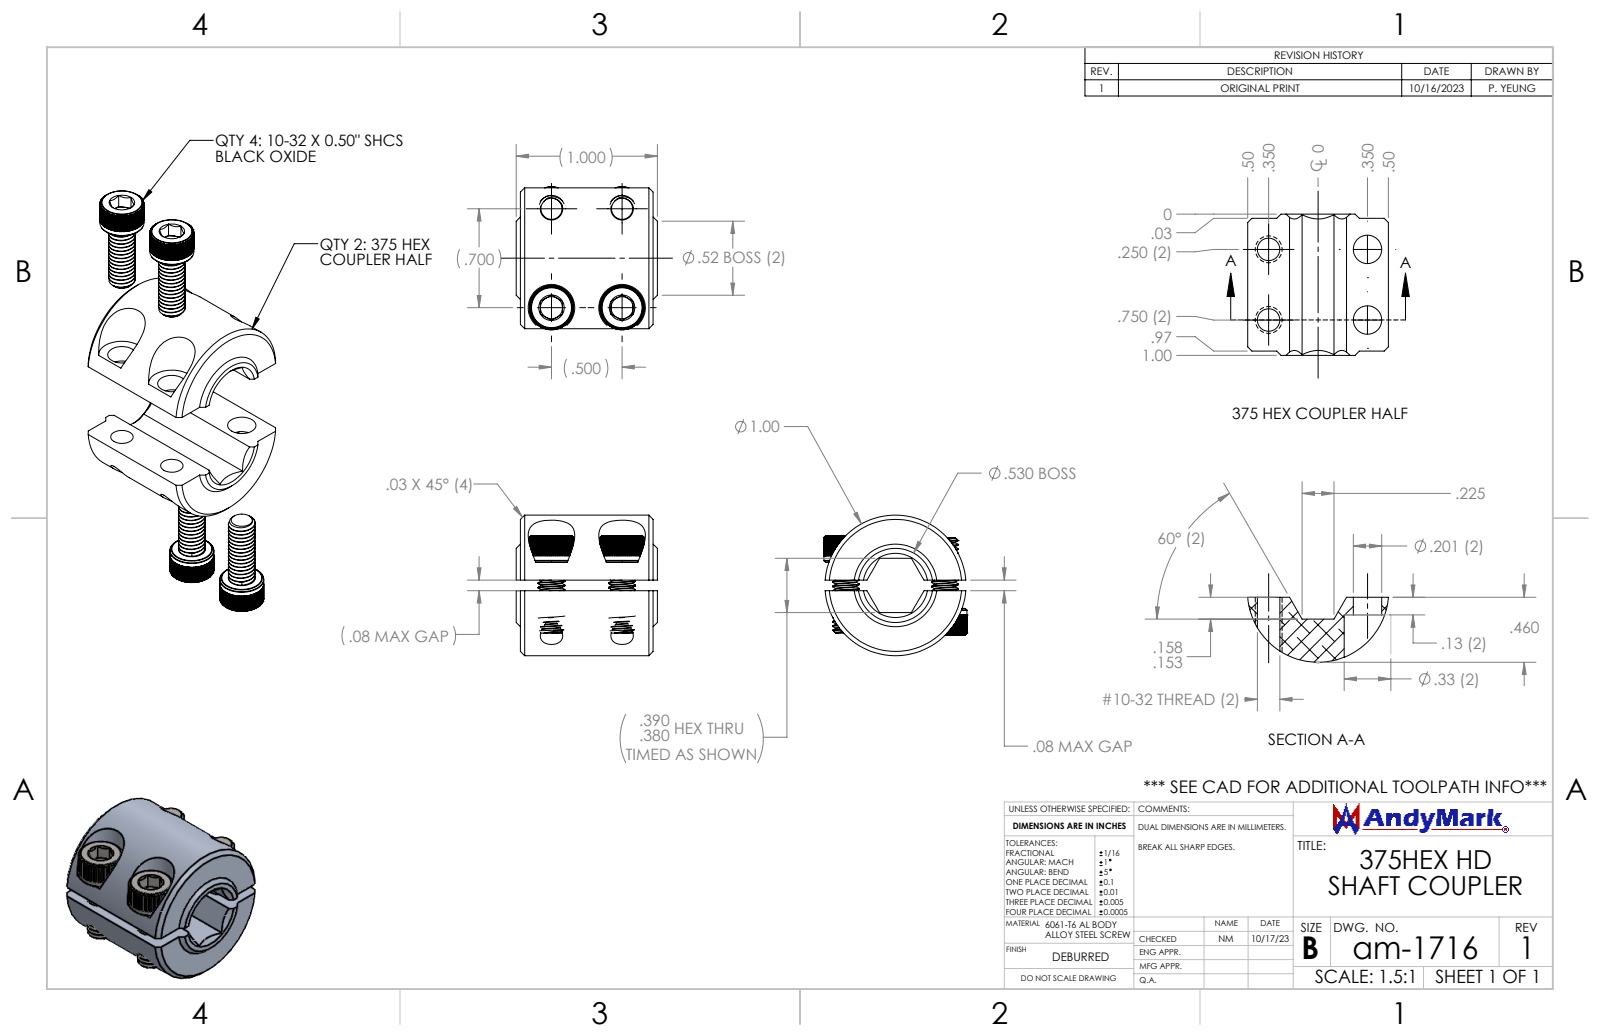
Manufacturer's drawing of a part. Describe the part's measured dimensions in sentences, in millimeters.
The part is named "375Hex Coupler Half; am-1716 375Hex Coupler; am-1002 10-32 x 0500 SHCS_am-1002 10-32 x 0500 SHCS". Its 3-D file was written by "SolidWorks 2022 (CONFIG_CONTROL_DESIGN)". It is 6 solids with 1808 faces: 658 planar, 450 cylindrical and 700 other. Overall it measures 25.7 by 25.4 by 25.3 millimeters. Its volume is 9 310 cubic millimeters and its surface area 6 935 square millimeters. Round holes: 4 of diameter 4, 4 of diameter 5.1. Round bosses or shafts: 4 of diameter 8, 4 of diameter 4.8. Partial cylindrical surfaces (rounded edges, fillets, slot ends): 4 of radius 4.2, 2 of radius 12.7. The main face-to-face distances are 1.9, 5.8, 3.9, 0.8, 23.9, 9.8, 5.1, 9, 3.2, 9.8. The hole center spacings are 12.7, 17.8, 21.9.
